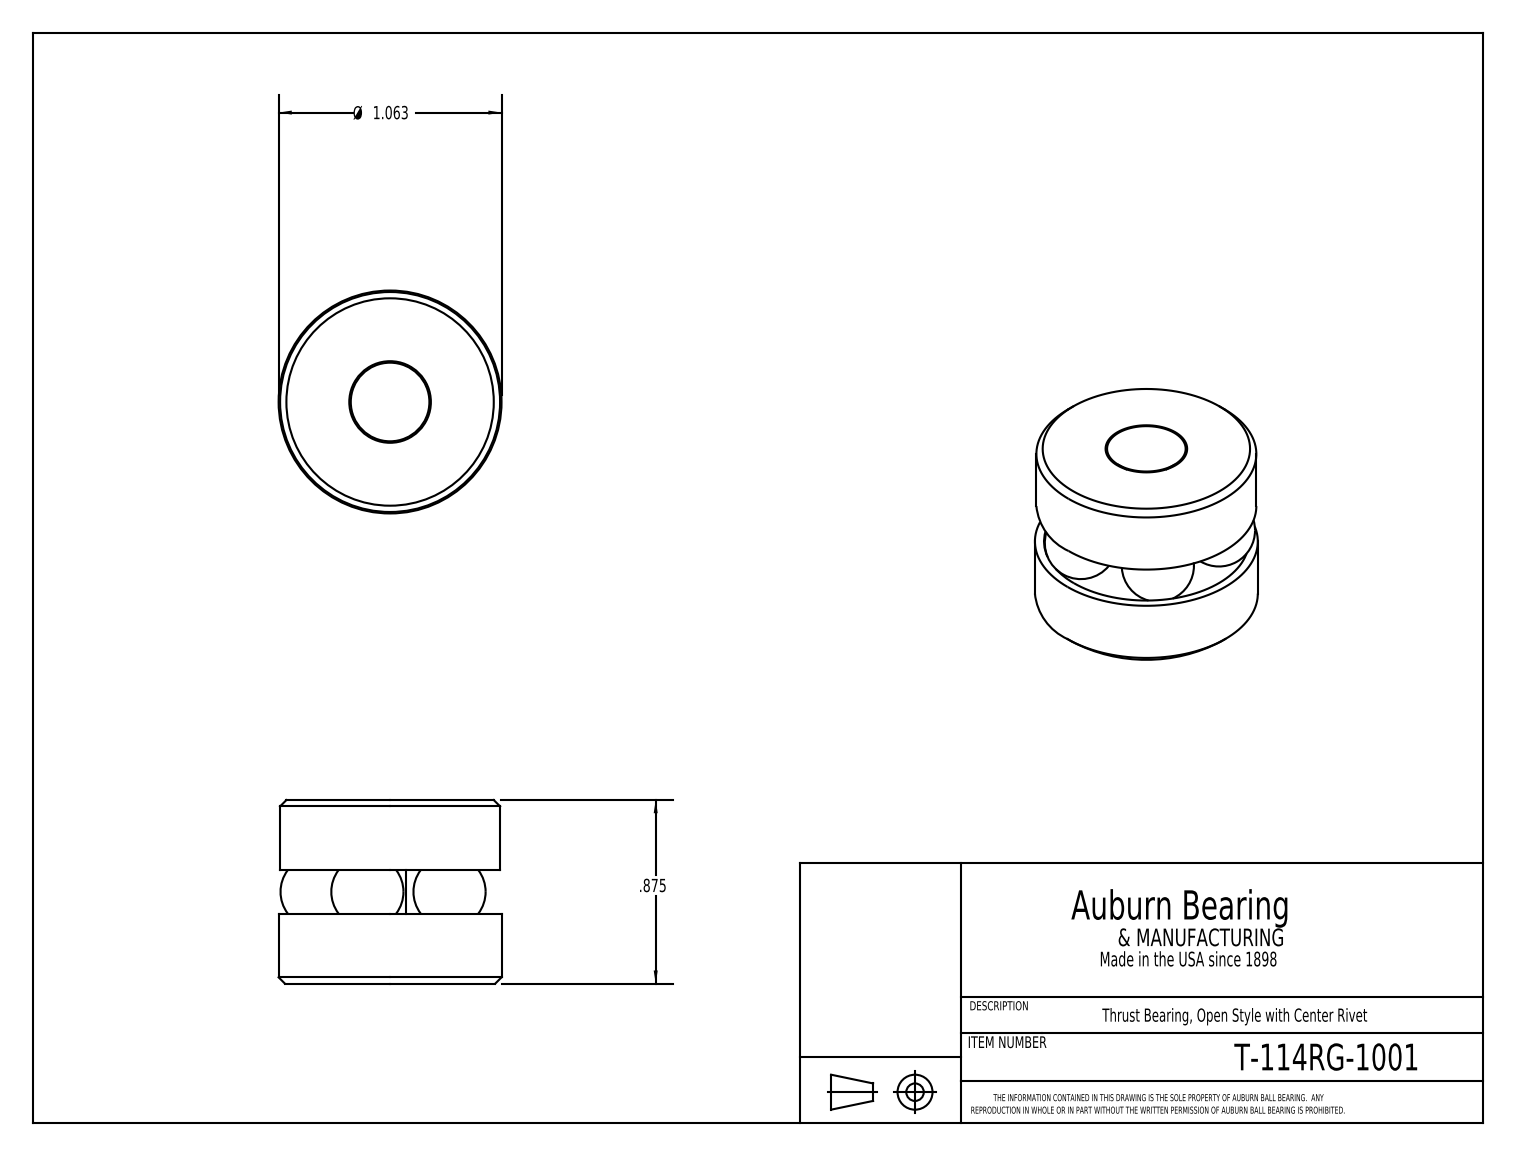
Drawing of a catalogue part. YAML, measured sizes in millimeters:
part_name: "T-114RG_T-114RG-1001"
step_written_by: "SolidWorks 2016 (CONFIG_CONTROL_DESIGN)"
units: millimeters
bodies: {solids: 8, faces: 26, planar: 8, cylindrical: 5, other: 13}
overall_size: [27, 27, 22.2]
volume: 10400
surface_area: 5597
round_holes:
  - {diameter: 4.2, count: 1}
round_bosses_or_shafts:
  - {diameter: 27, count: 1}
  - {diameter: 26.6, count: 1}
  - {diameter: 4, count: 1}
face_to_face_distances: [22.2, 8.5, 13.7, 5.2, 22.2, 13.7, 8.5]
